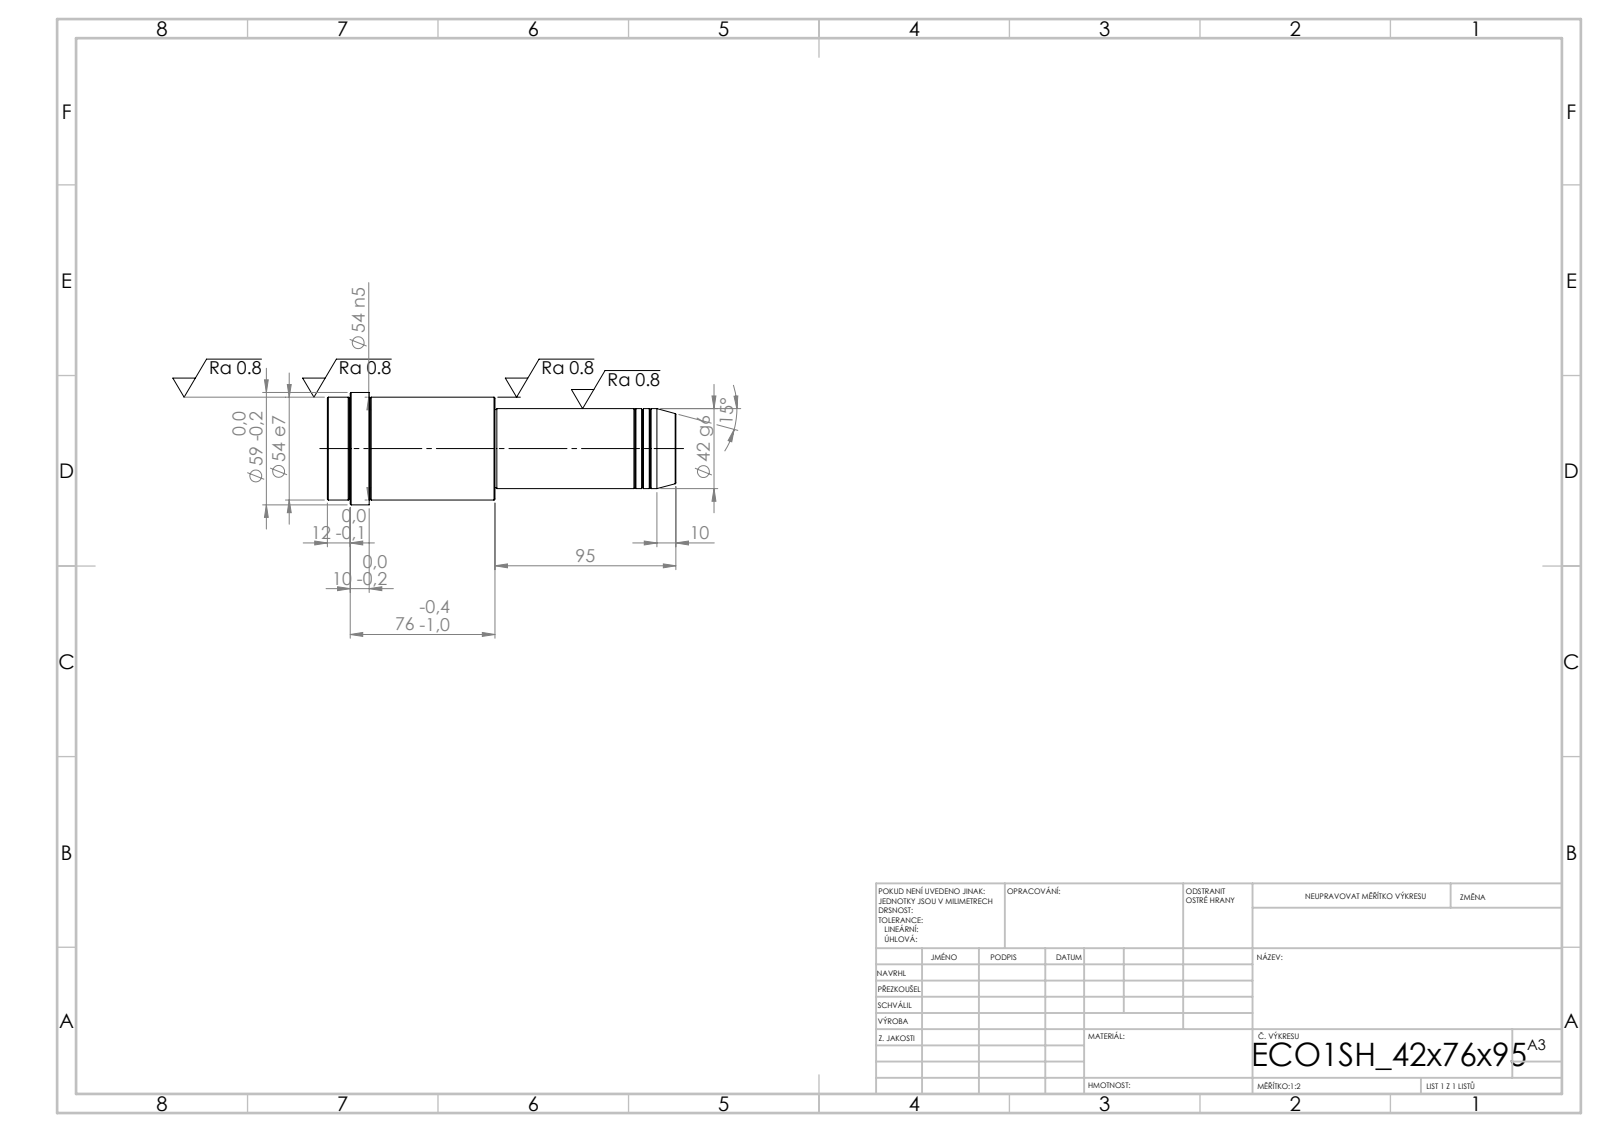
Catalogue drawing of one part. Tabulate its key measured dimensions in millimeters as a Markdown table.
| quantity | value |
| --- | --- |
| STEP written by | SolidWorks 2019 (CONFIG_CONTROL_DESIGN) |
| units | millimeters |
| bodies | 1 solid, 52 faces (6 planar, 16 cylindrical, 30 other) |
| overall size | 183 × 59 × 59 |
| volume | 335 482 mm³ |
| surface area | 33 081 mm² |
| round bosses / shafts (diameter × count) | 59 × 1, 54 × 1, 42 × 1, 41 × 1 |
| main face-to-face distances | 183, 95, 88, 161, 66, 22, 171, 76, 10, 12 |
